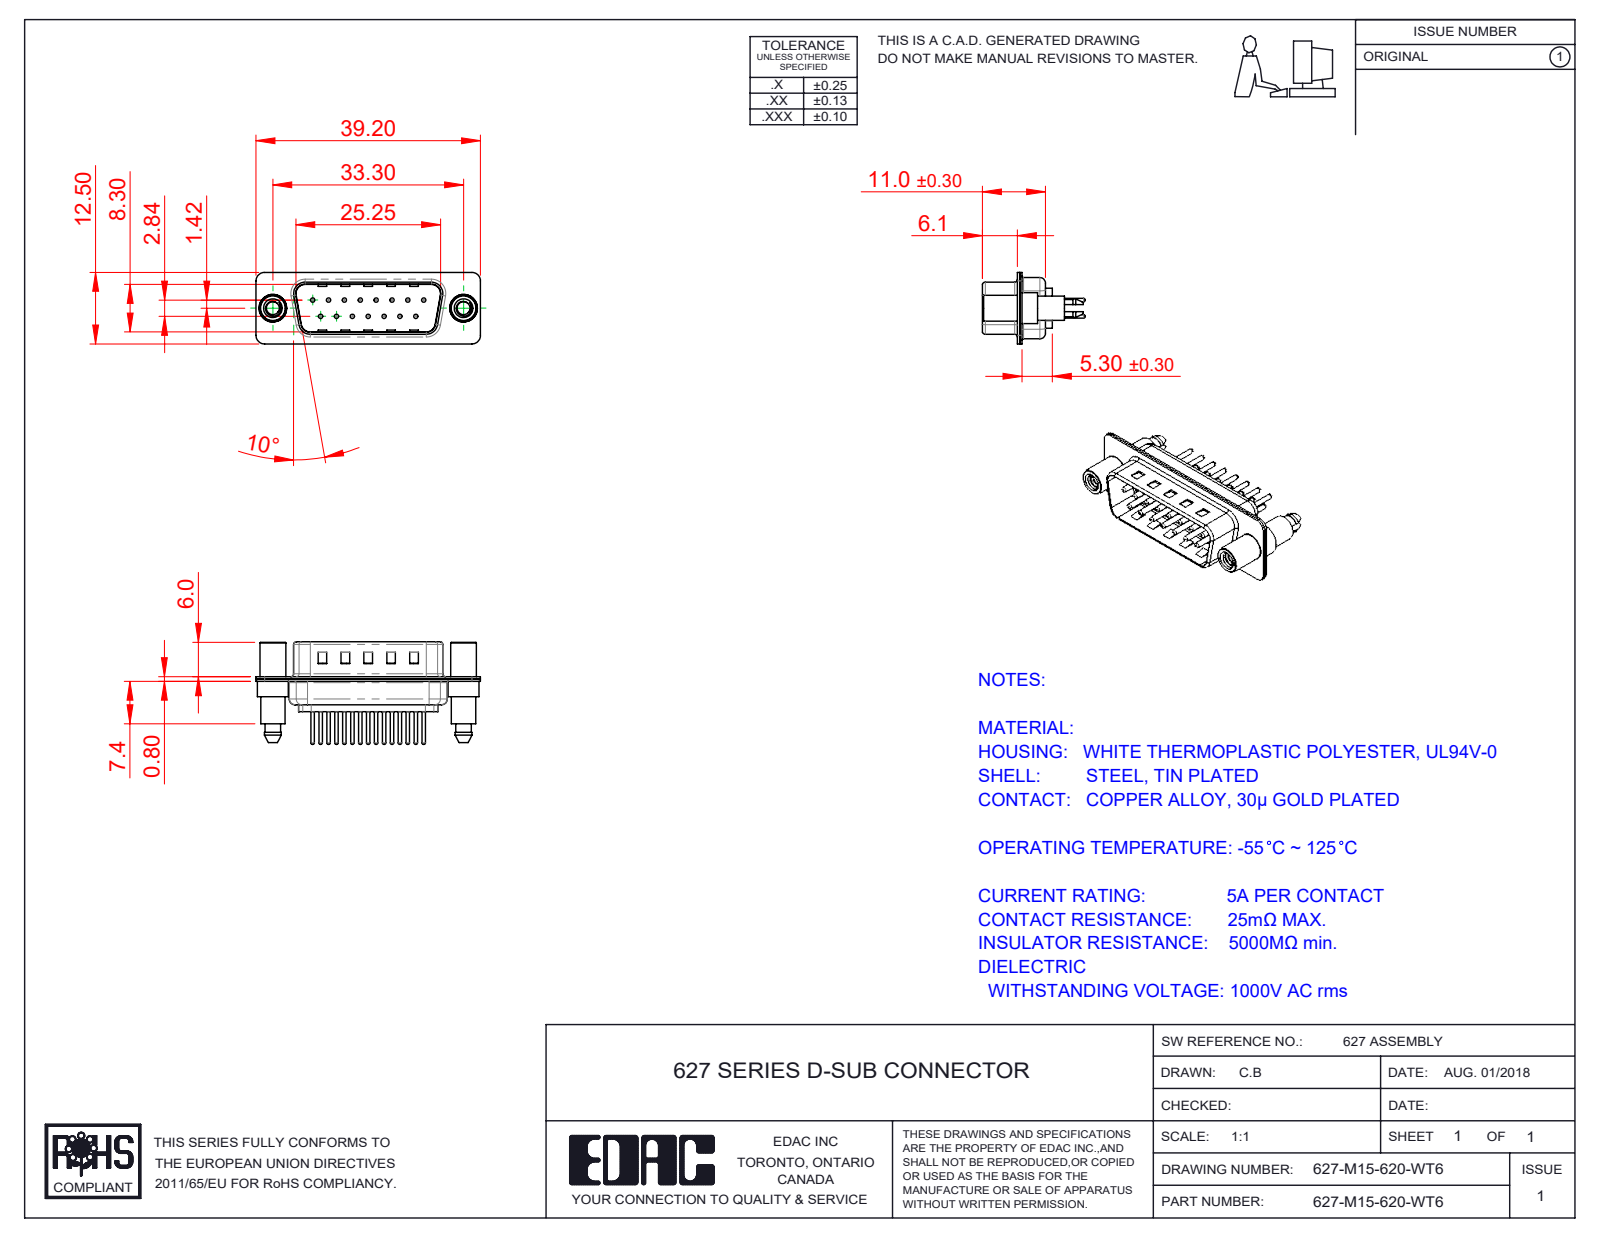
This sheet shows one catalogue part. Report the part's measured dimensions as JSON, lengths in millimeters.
{"part_name": "627M Shell Front_15 Contacts; 627M Housing_15 Contacts; 627M 4-40 Threaded Standoff and Boardlock; 627M Contact Row 2_20 (+3 more)", "step_written_by": "SolidWorks 2020 (CONFIG_CONTROL_DESIGN)", "units": "millimeters", "bodies": {"solids": 20, "faces": 947, "planar": 262, "cylindrical": 371, "other": 314}, "overall_size": [39.2, 17.9, 12.5], "volume_mm3": 2182, "surface_area_mm2": 5276, "round_holes": [[0.75, 15], [1.6, 15], [2, 15], [2.26, 2], [4, 2], [4.8, 2]], "round_bosses_or_shafts": [[1.5, 15], [0.6, 15], [5.4, 2], [4.9, 2], [4.5, 2], [4.25, 2]], "partial_cylinders_radius": [[1.5, 18], [2, 12], [1.6, 10], [0.5, 8], [0.25, 4], [0.6, 4], [0.65, 4], [0.9, 4]], "face_to_face_distances": [0.4, 0.8, 9.5, 9.1, 8.7, 9.9, 5.3, 1.2, 6.1, 5.7], "hole_center_spacings": [3.16, 2.77, 5.54, 8.31, 11.08, 5.03, 5.04, 7.48]}
